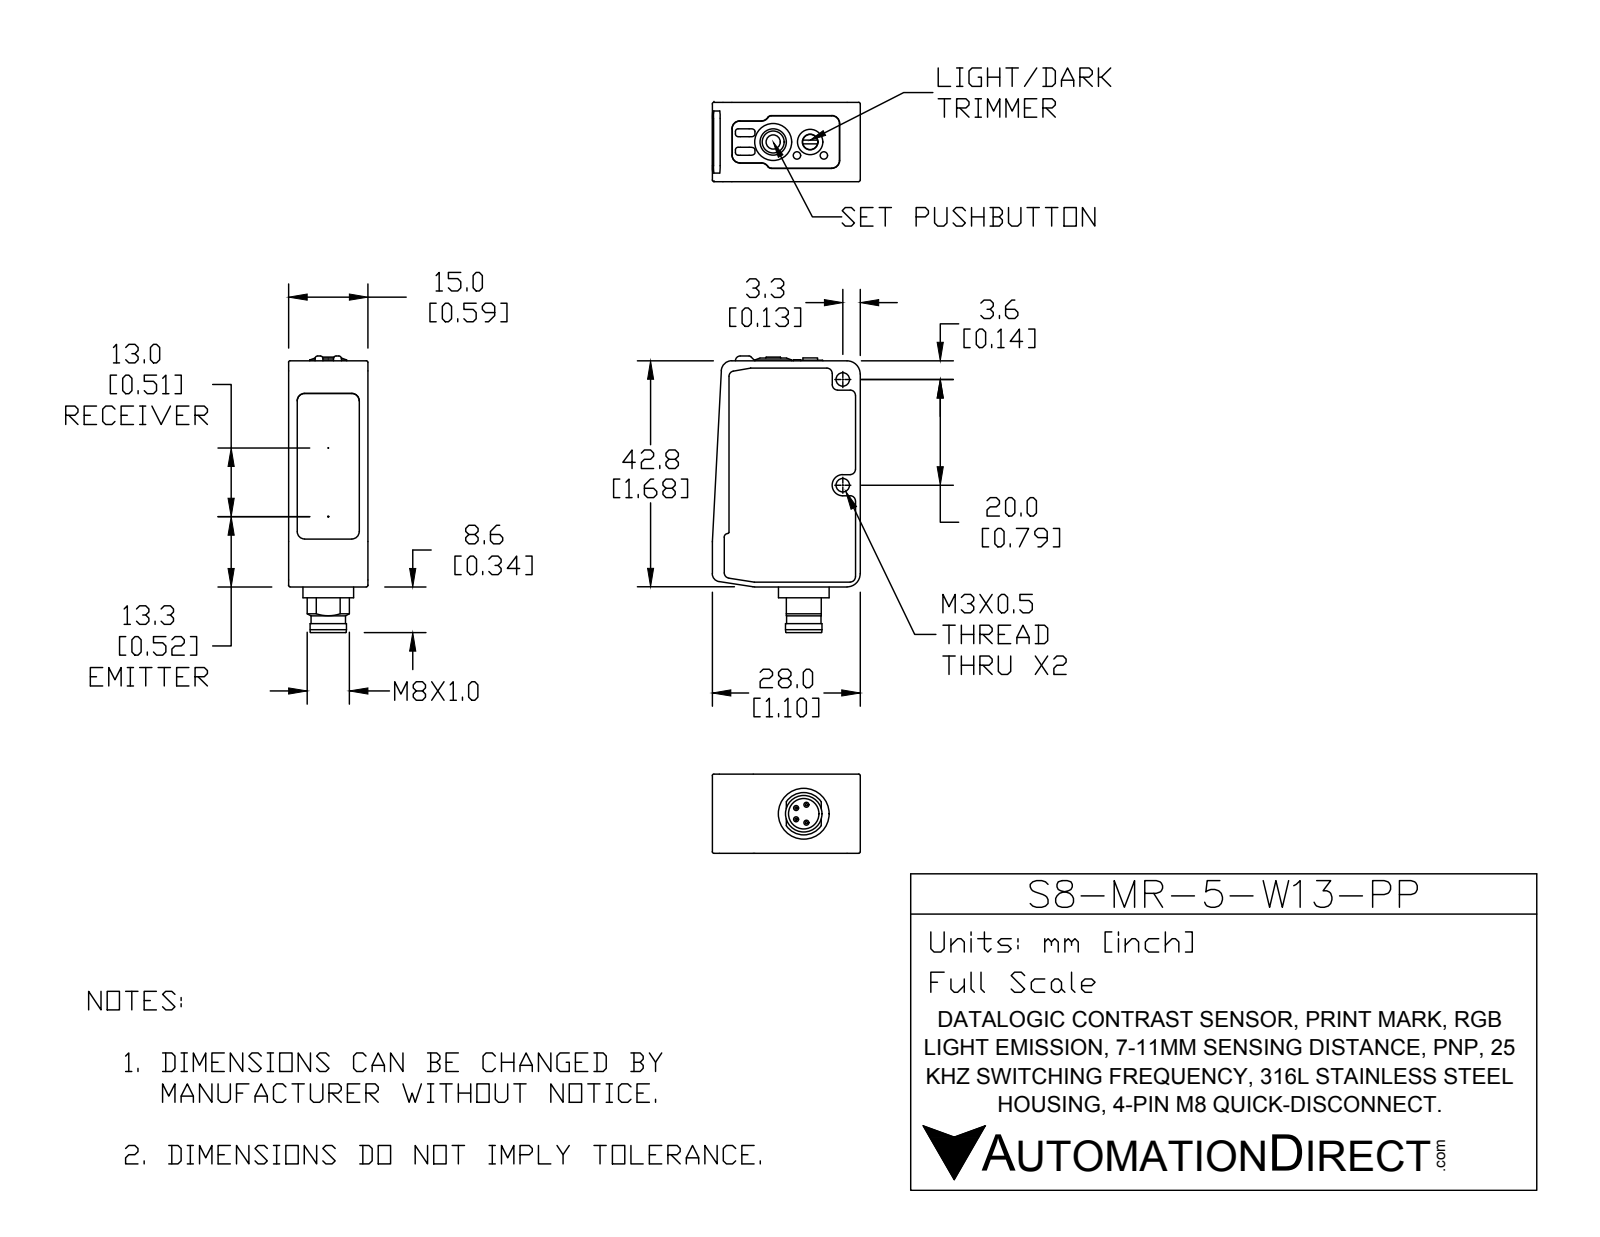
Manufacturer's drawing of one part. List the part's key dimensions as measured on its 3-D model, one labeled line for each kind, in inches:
Part name (STEP PRODUCT): S8-MR-5-W13-PP
STEP written by: SolidWorks 2016 (AUTOMOTIVE_DESIGN)
Units: inches
Bodies: 9 solids, 250 faces (66 planar, 107 cylindrical, 77 other)
Overall size (bounding box): 2.061 × 1.102 × 0.591
Volume: 1.069 in³ · Surface area: 8.702 in²
Round holes (diameter × count): ⌀0.1 ×2, ⌀0.055 ×1, ⌀0.116 ×1, ⌀0.227 ×1
Round bosses / shafts (diameter × count): ⌀0.037 ×4, ⌀0.378 ×1, ⌀0.276 ×1, ⌀0.272 ×1, ⌀0.257 ×1, ⌀0.112 ×1, ⌀0.106 ×1, ⌀0.055 ×1
Partial cylindrical surfaces — rounded edges, fillets, slot ends (radius × count): R0.012 ×23, R0.02 ×9, R0.059 ×7, R0.008 ×6, R0.055 ×4, R0.057 ×4, R0.028 ×2, R0.03 ×2
Main face-to-face distances: 0.591, 1.642, 0.043, 1.685, 1.102, 0.551, 0.207, 1.848, 1.892, 0.098
Hole centre spacings: 0.048, 0.143, 0.181, 0.512, 0.787
